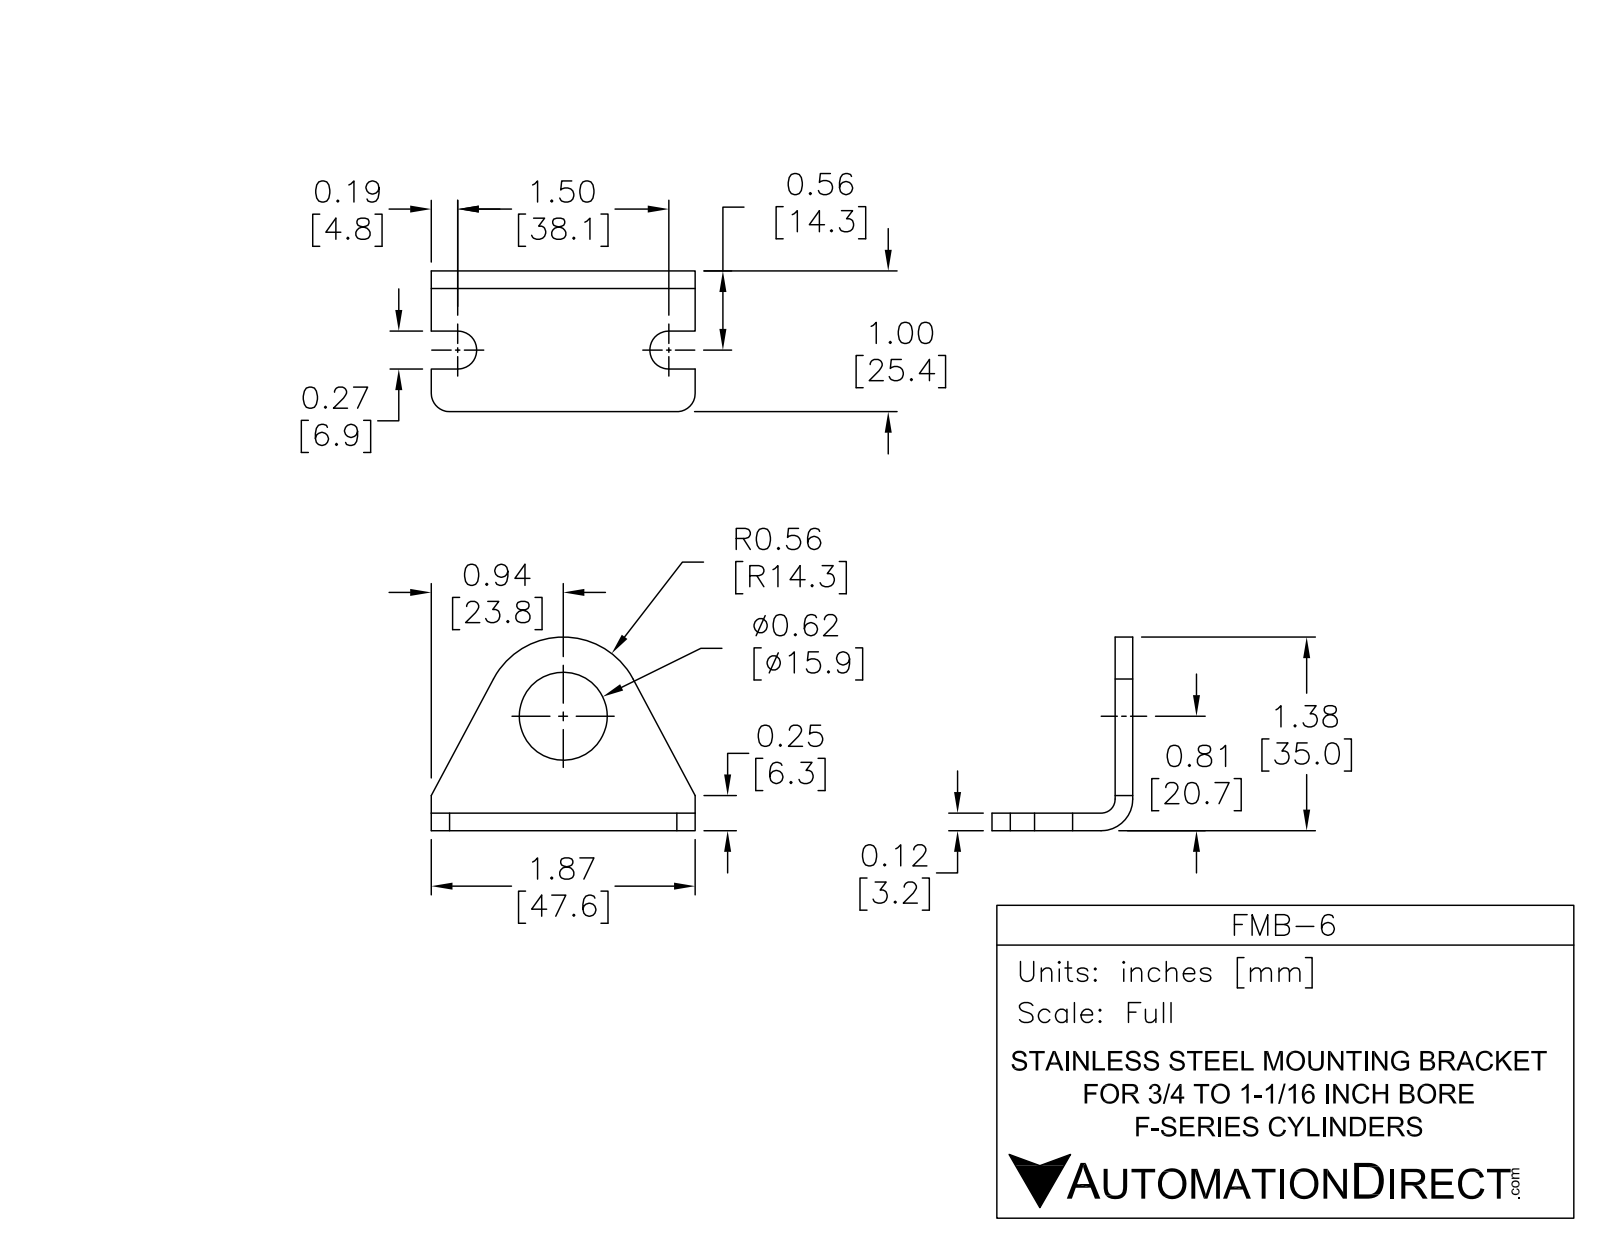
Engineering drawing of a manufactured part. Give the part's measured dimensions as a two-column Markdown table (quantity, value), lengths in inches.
| quantity | value |
| --- | --- |
| part name | FMB-6 |
| STEP written by | SolidWorks 2017 (AUTOMOTIVE_DESIGN) |
| units | inches |
| bodies | 1 solid, 28 faces (19 planar, 9 cylindrical, 0 other) |
| overall size | 1.874 × 1.378 × 1 |
| volume | 0.369 in³ |
| surface area | 7.153 in² |
| round holes (diameter × count) | 0.626 × 1 |
| partial cylindrical surfaces (radius × count) | 0.135 × 2, 0.187 × 2, 0.03 × 1, 0.155 × 1, 0.56 × 1 |
| main face-to-face distances | 0.125, 0.125, 0.875, 1, 1.874, 0.302, 0.573, 0.698, 0.572, 0.27 |
